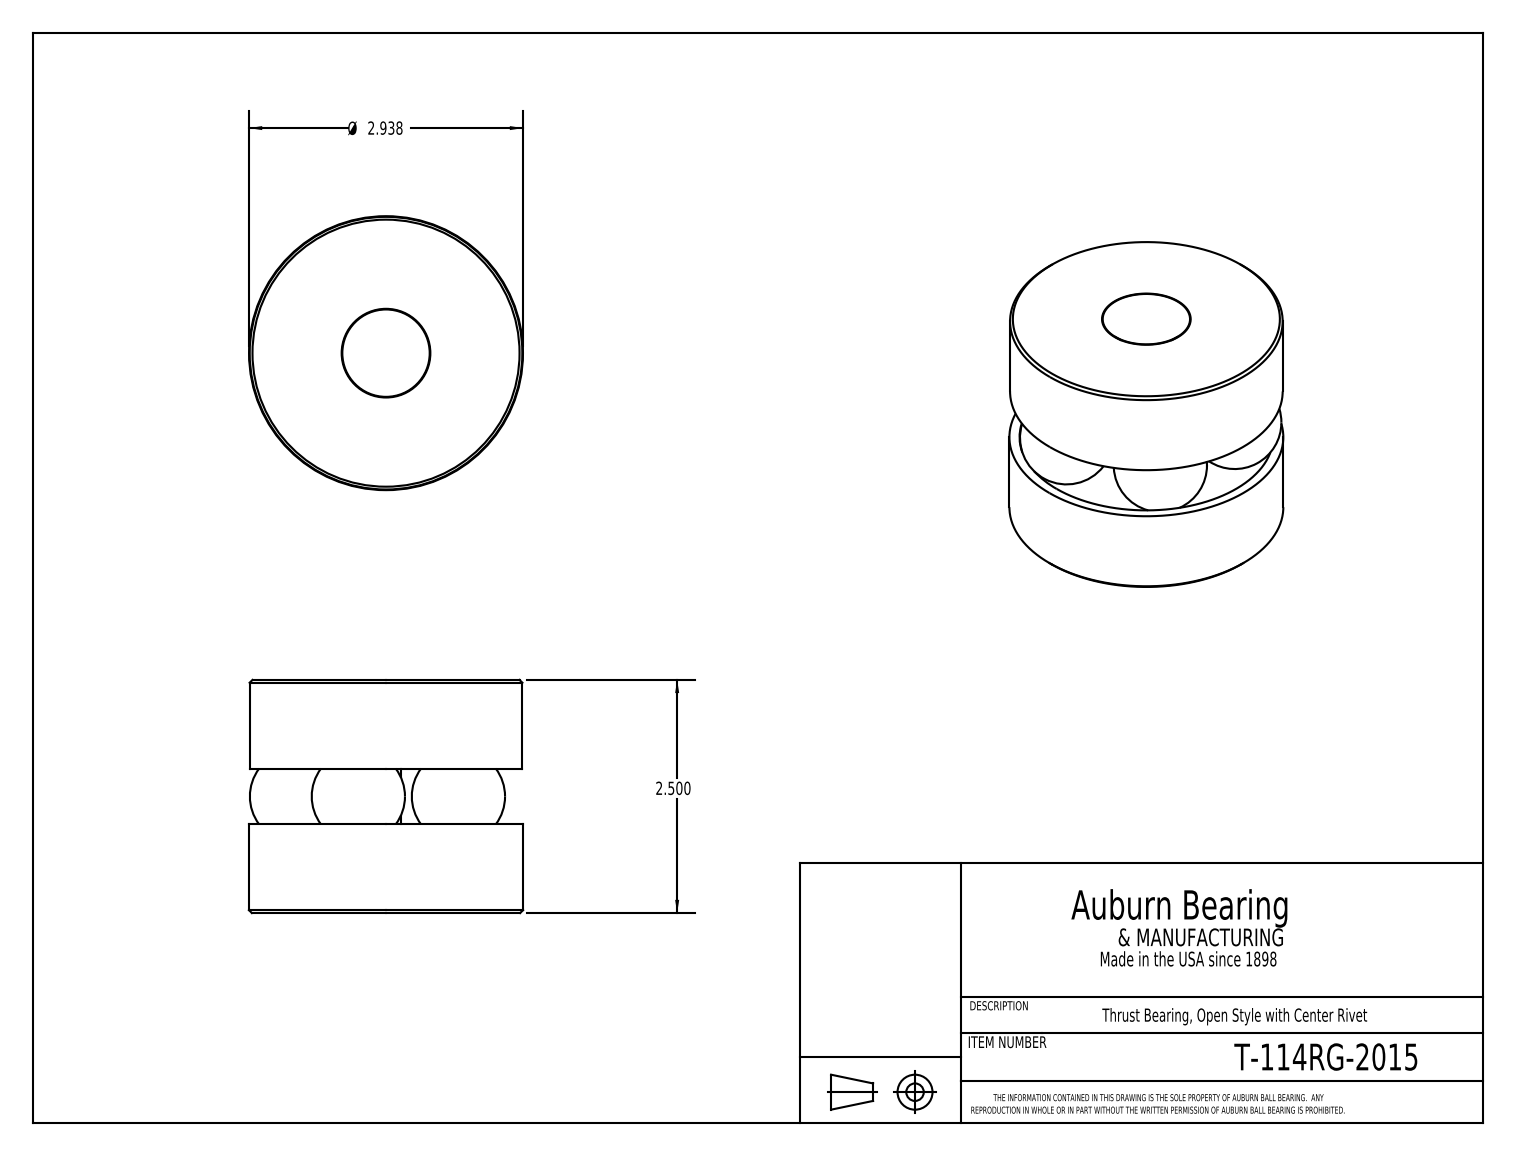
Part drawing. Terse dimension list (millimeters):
name: T-114RG_T-114RG-2015
written by: SolidWorks 2016 (CONFIG_CONTROL_DESIGN)
unit: mm
bodies: 8 solids, 26 faces (8 planar, 5 cylindrical, 13 other)
size: 74.6 × 74.6 × 63.5
volume: 231 200 mm³; area: 43 760 mm²
holes: 1× ⌀8.2
bosses: 1× ⌀74.6, 1× ⌀74.3, 1× ⌀7.9
face distances: 63.5, 24.1, 39.4, 15.2
